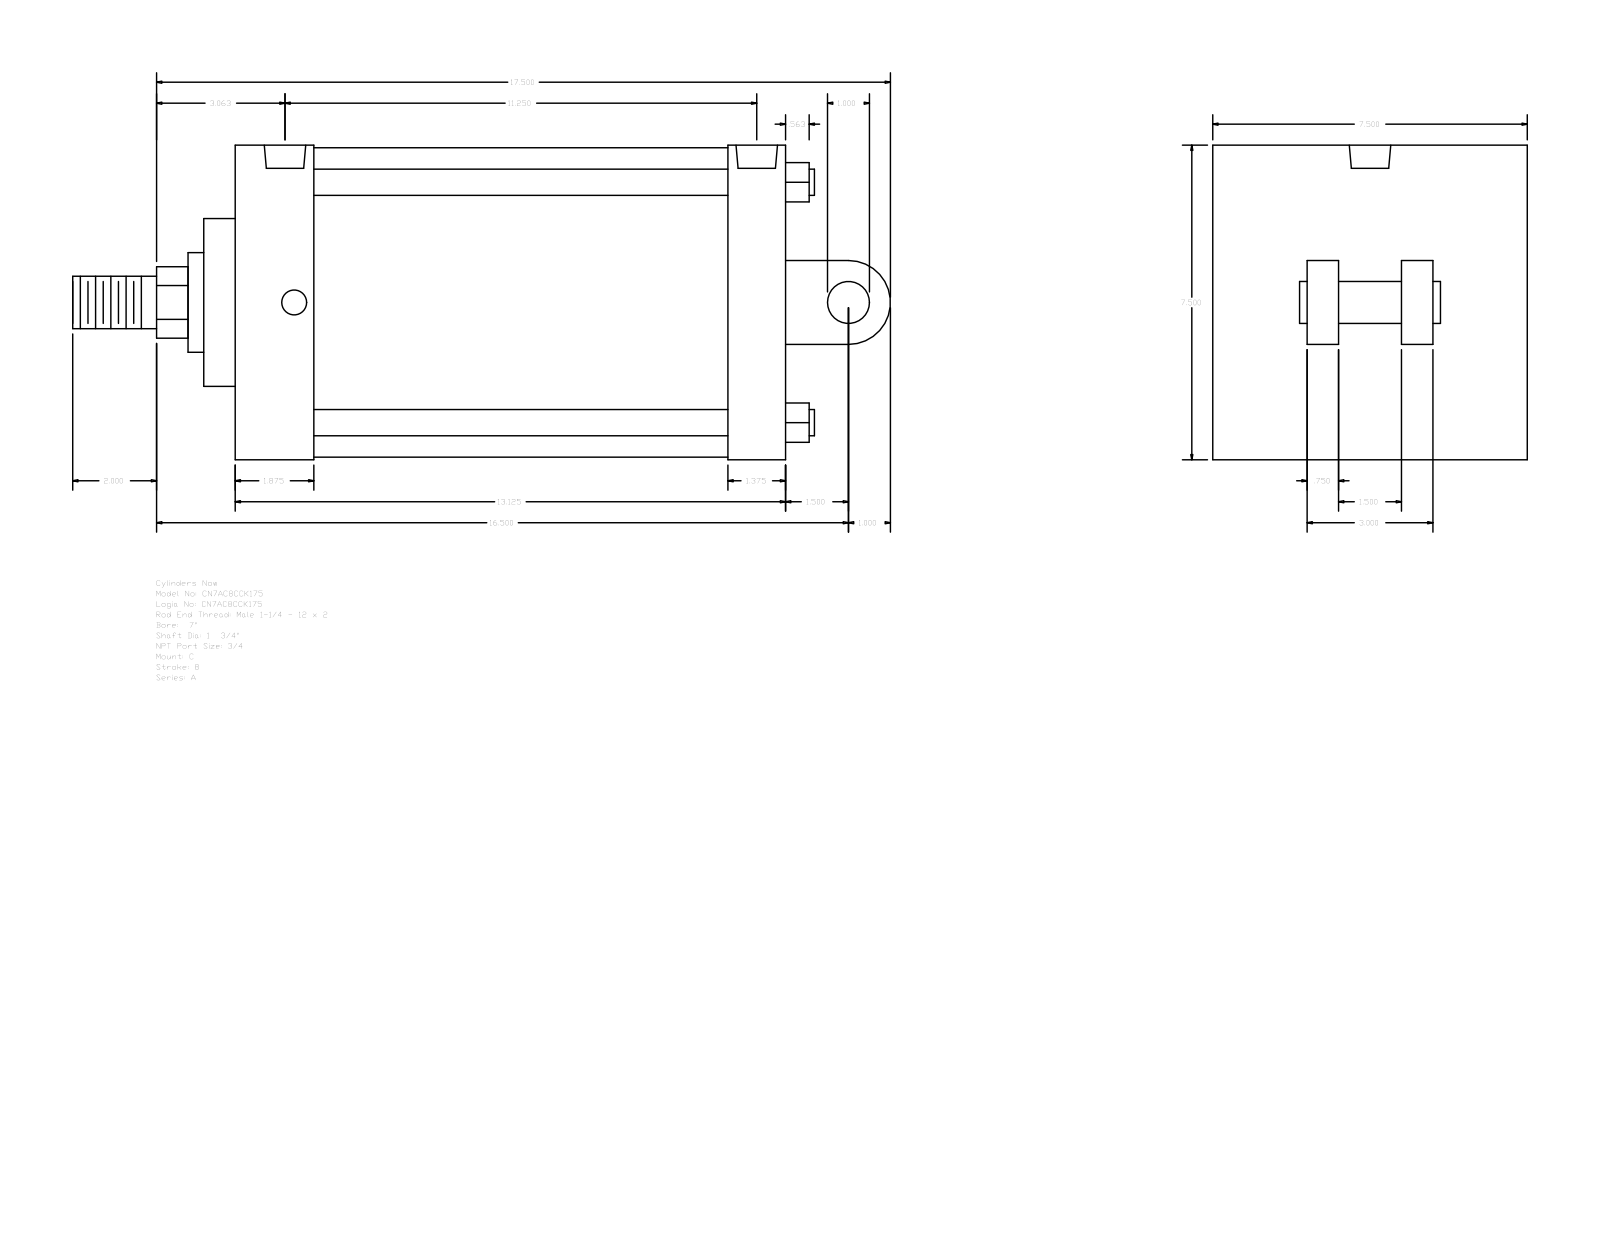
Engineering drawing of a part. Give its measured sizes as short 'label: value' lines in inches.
name: A_C__0700_1.75
written by: GSSL Pune (CONFIG_CONTROL_DESIGN)
unit: in
bodies: 0 solids, 104 faces (75 planar, 29 cylindrical, 0 other)
size: 19.5 × 7.5 × 7.5
holes: 4× ⌀0.594, 2× ⌀0.989
bosses: 4× ⌀0.625, 1× ⌀7.375, 1× ⌀2.375, 1× ⌀1.75, 1× ⌀1.25, 1× ⌀1
rounds: 1× R0.852, 1× R1
face distances: 7.5, 13.125, 0.75, 3, 2.25, 5.75, 1.75, 2.75, 1.875, 11.25
hole spacings: 0.219, 10.812, 11.031, 11.25
